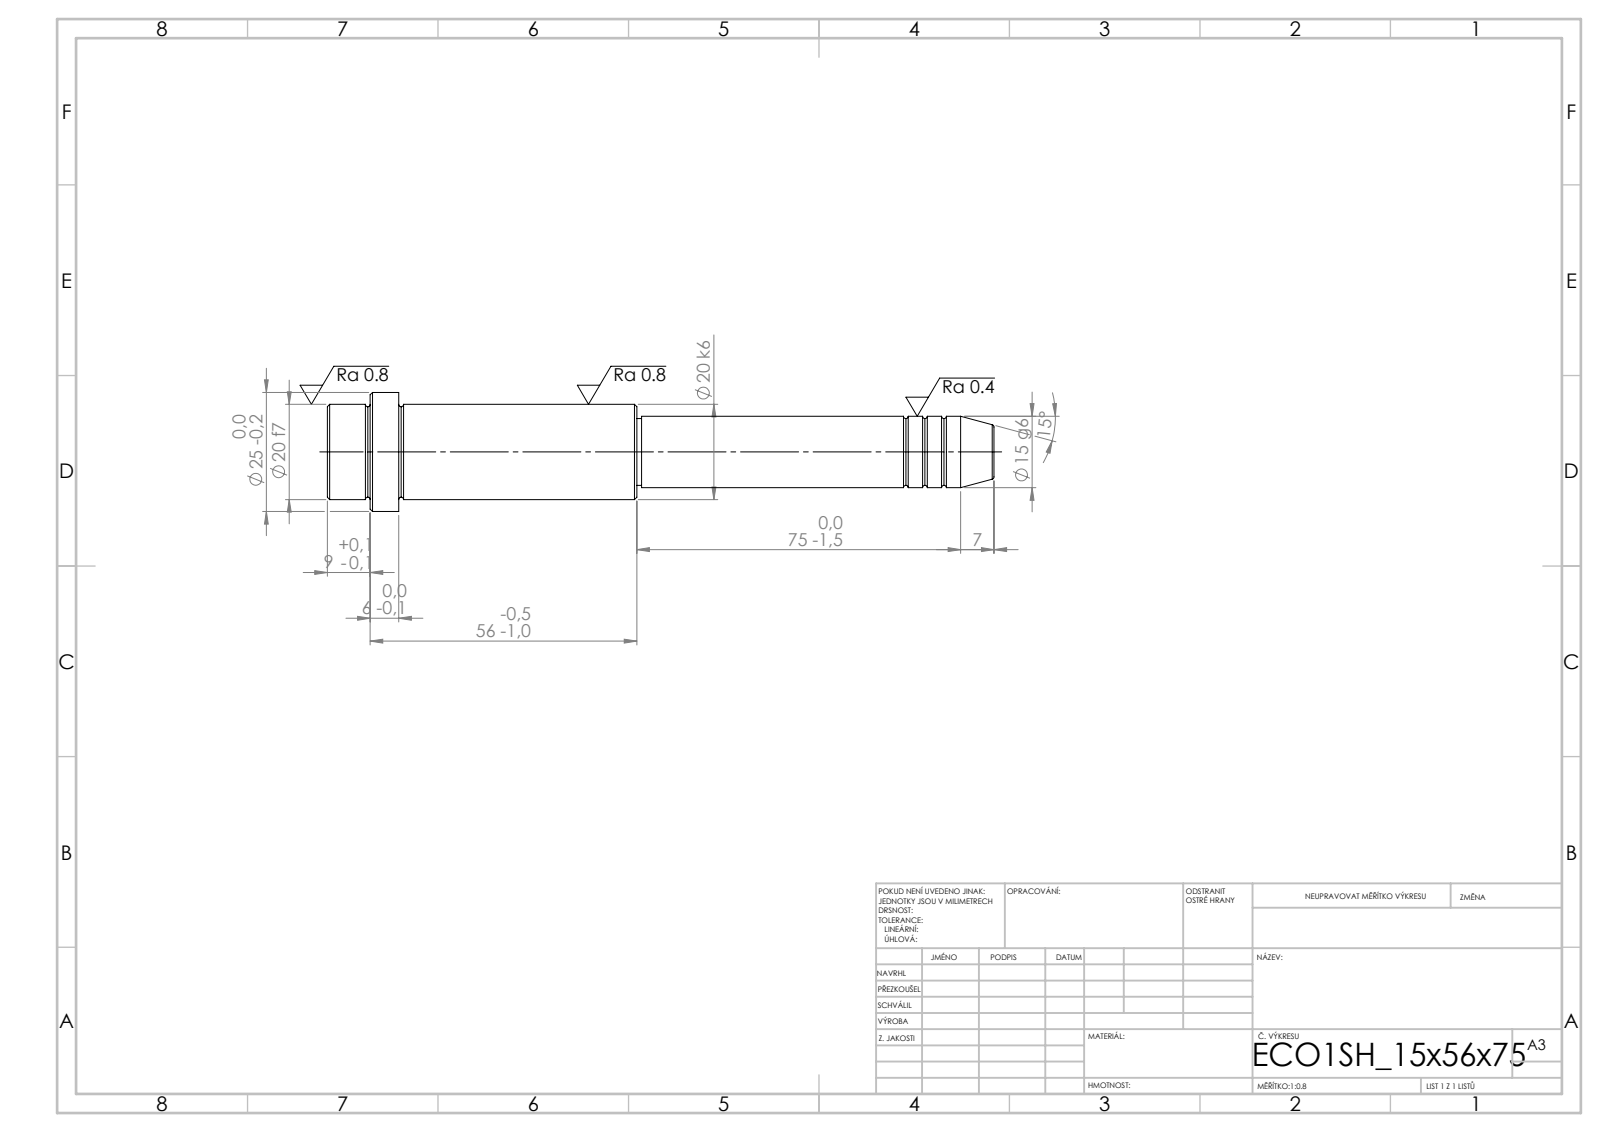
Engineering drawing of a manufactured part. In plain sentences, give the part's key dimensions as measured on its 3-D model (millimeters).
Its 3-D file was written by "SolidWorks 2019 (CONFIG_CONTROL_DESIGN)". It is 1 solid with 52 faces: 6 planar, 16 cylindrical and 30 other. Overall it measures 140 by 25 by 25 millimeters. Its volume is 34 300 cubic millimeters and its surface area 8 700 square millimeters. Round bosses or shafts: 1 of diameter 25, 1 of diameter 20, 1 of diameter 15, 1 of diameter 14. The main face-to-face distances are 15, 6, 9, 50, 56, 65, 75, 125, 131, 140.
